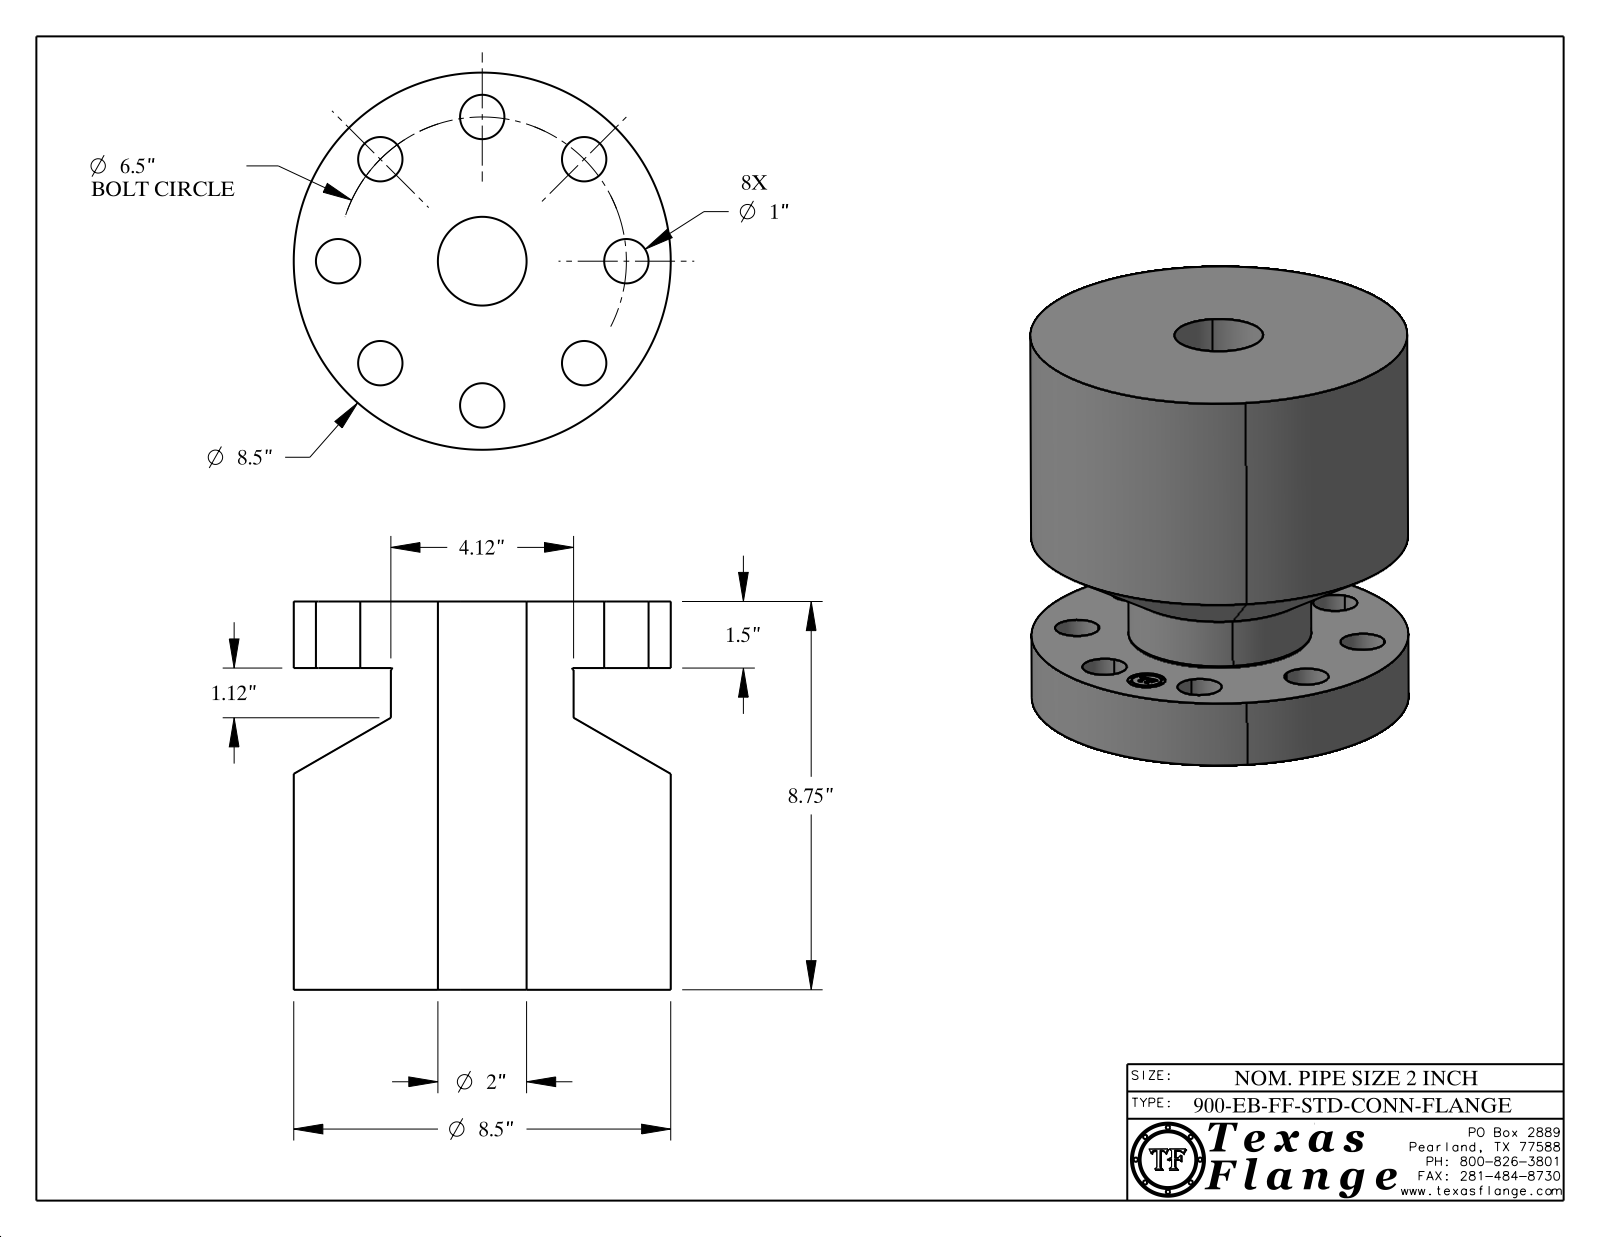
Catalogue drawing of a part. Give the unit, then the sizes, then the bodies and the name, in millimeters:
Units: millimetres
Overall size (bounding box): 222.3 × 215.9 × 215.9
Round holes (diameter × count): ⌀25.4 ×8, ⌀21.6 ×1, ⌀50.8 ×1
Round bosses / shafts (diameter × count): ⌀1.3 ×8, ⌀215.9 ×1, ⌀104.6 ×1, ⌀17 ×1
Main face-to-face distances: 222.3, 38.1, 184.2, 38, 184.3, 6.5, 6.3, 0.4, 1.2, 4.2
Hole centre spacings: 82.6, 63.2, 116.7, 152.5, 165.1, 32.2, 137.3, 161.9
Volume: 6 232 000 mm³ · Surface area: 300 600 mm²
Bodies: 1 solid, 418 faces (368 planar, 44 cylindrical, 6 other)
Part name (STEP PRODUCT): 2-900-EB-FF-STD-CONN-FLANGE
STEP written by: CATIA V5 STEP AP214 (AUTOMOTIVE_DESIGN)
